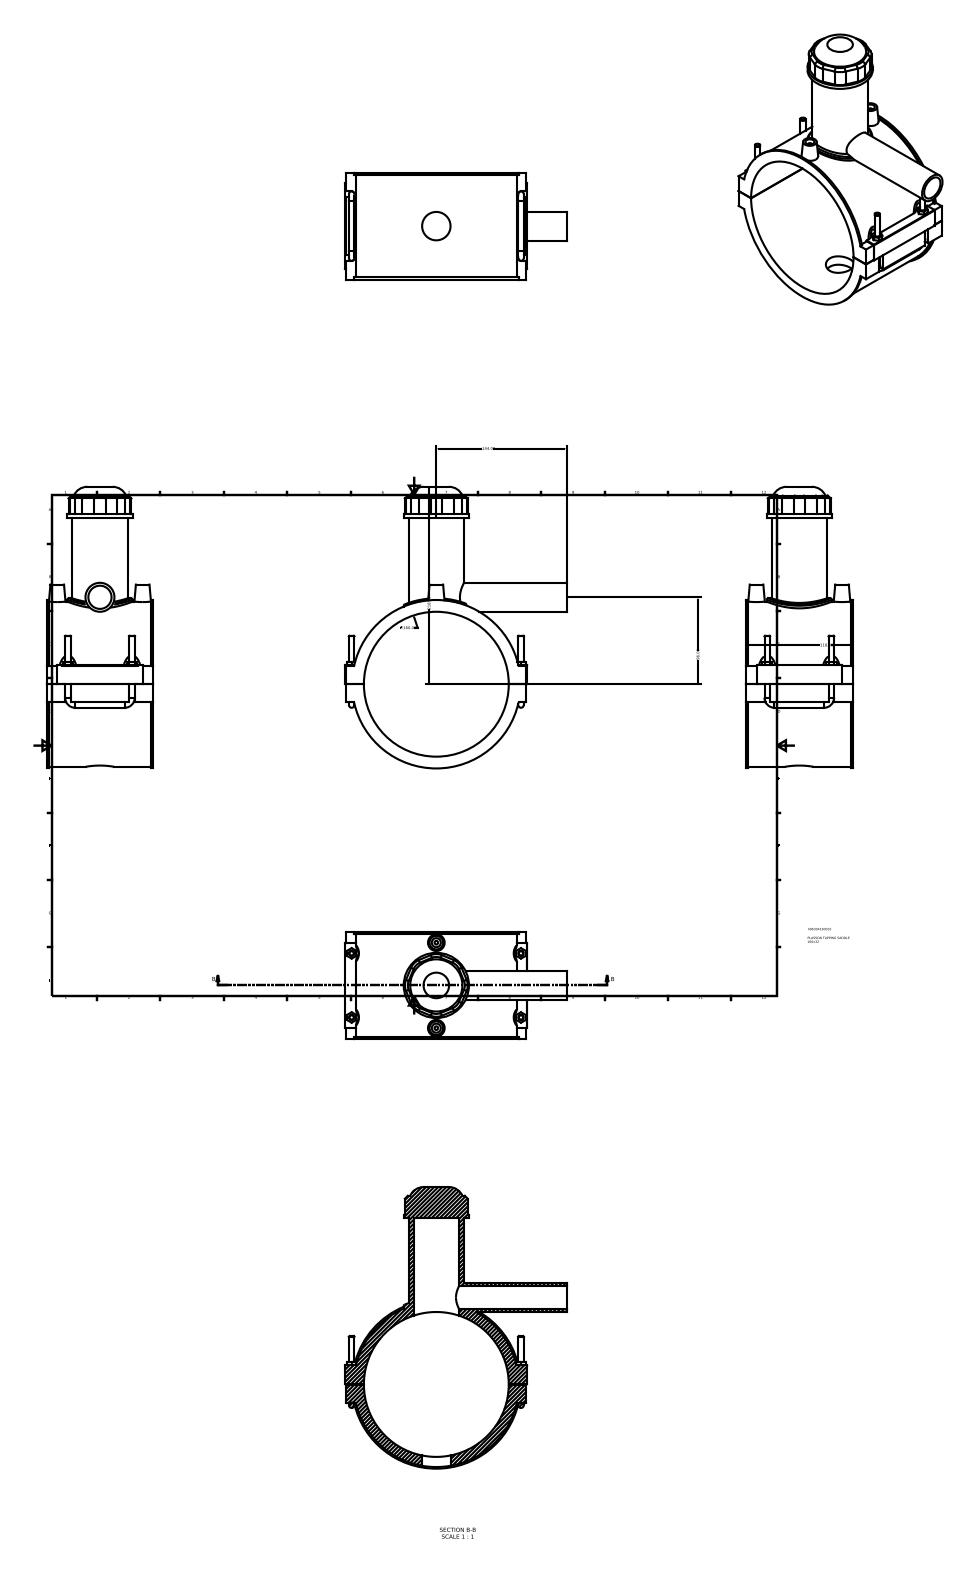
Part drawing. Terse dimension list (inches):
name: 496304160032
written by: Autodesk Inventor 2015 (AUTOMOTIVE_DESIGN)
unit: in
bodies: 1 solid, 181 faces (110 planar, 47 cylindrical, 24 other)
size: 12.245 × 9.626 × 4.646
volume: 62.24 in³; area: 358 in²
holes: 2× ⌀0.394, 1× ⌀1.008, 1× ⌀1.235, 1× ⌀1.984, 1× ⌀6.299
bosses: 6× ⌀0.236, 2× ⌀0.157, 1× ⌀7.325, 1× ⌀7.181, 1× ⌀2.835, 1× ⌀2.409, 1× ⌀1.26
rounds: 8× R0.63, 4× R0.118, 4× R0.295, 1× R0.02, 1× R3.734
face distances: 4.646, 0.039, 7.874, 7.226, 7.222, 7.835, 0.785, 0.789, 8.012, 7.913
hole spacings: 1.858, 3.717
